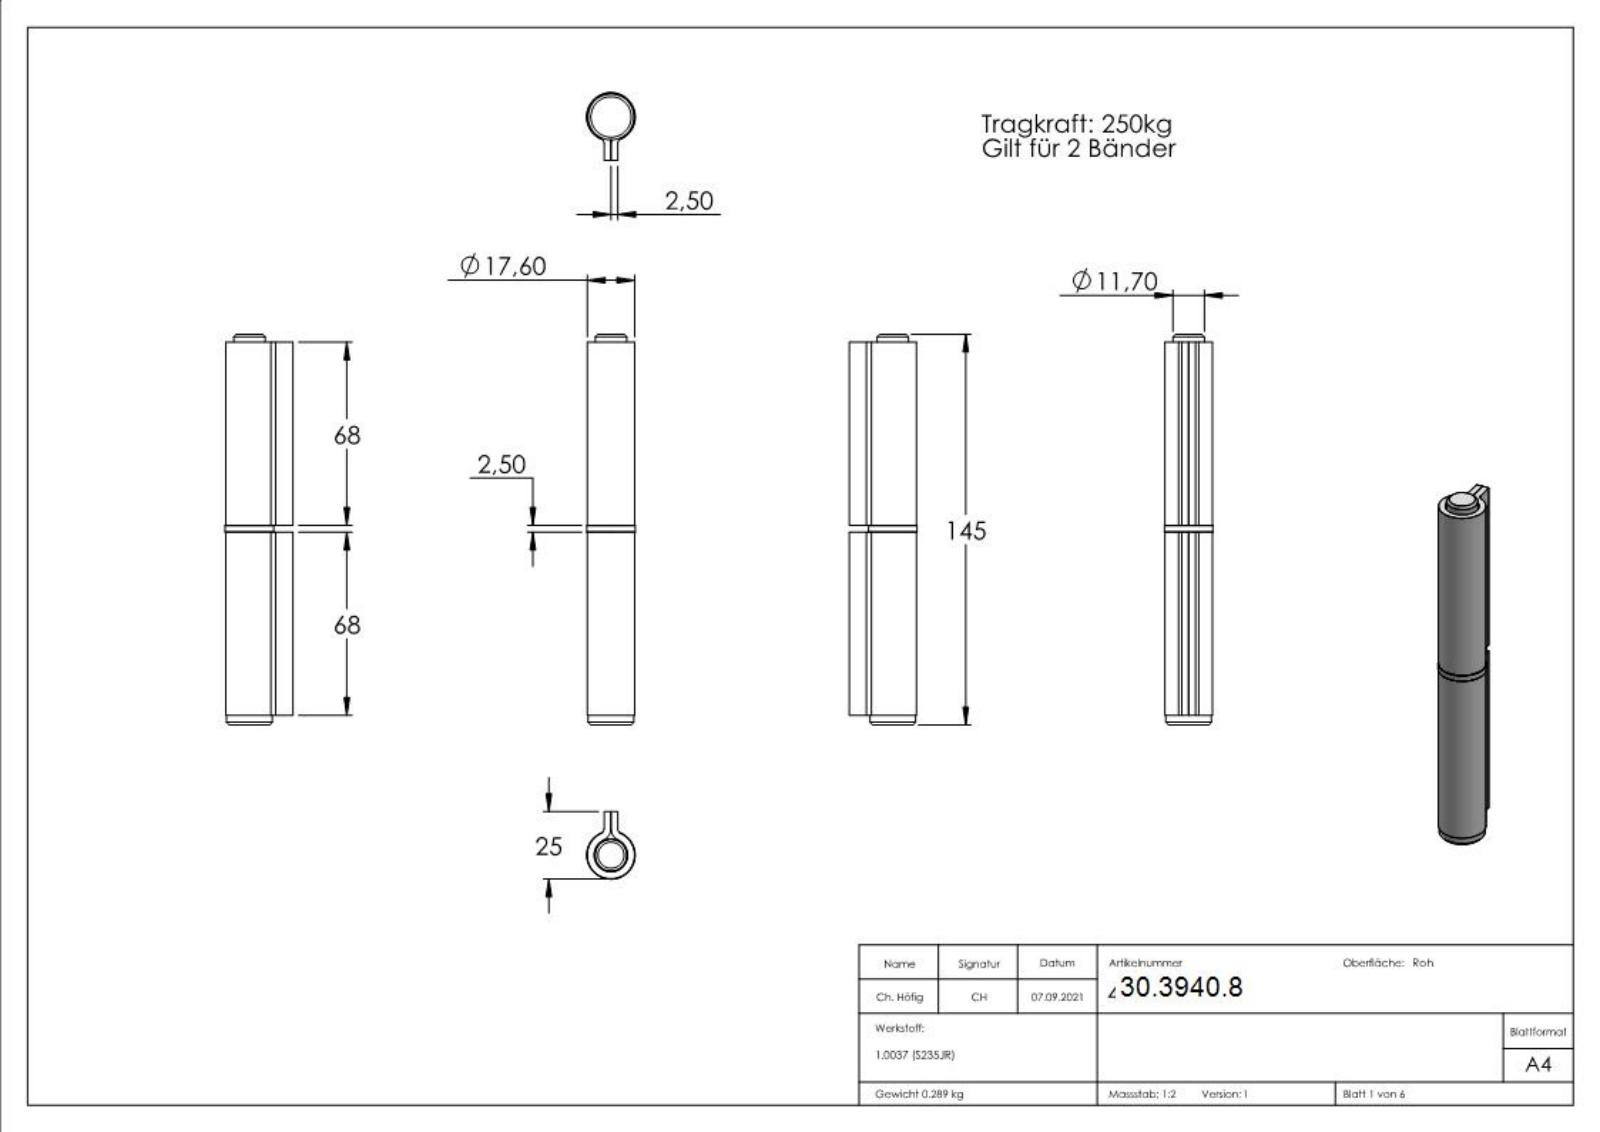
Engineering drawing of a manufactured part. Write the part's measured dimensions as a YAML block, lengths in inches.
part_name: "405-xx Teil1_405-14 Teil1; 405-14; 405-xx Teil1; 405-xx Teil3_405-14 Teil3 (+5 more)"
step_written_by: "SolidWorks 2018 (CONFIG_CONTROL_DESIGN)"
units: inches
bodies: {solids: 4, faces: 310, planar: 161, cylindrical: 38, other: 111}
overall_size: [5.709, 0.992, 0.709]
volume: 2.263
surface_area: 37.52
round_holes:
  - {diameter: 0.472, count: 1}
  - {diameter: 0.496, count: 1}
round_bosses_or_shafts:
  - {diameter: 0.709, count: 1}
  - {diameter: 0.693, count: 1}
  - {diameter: 0.669, count: 1}
  - {diameter: 0.461, count: 1}
partial_cylinders:
  - {radius: 0.079, count: 2}
  - {radius: 0.177, count: 2}
  - {radius: 0.252, count: 1}
face_to_face_distances: [0.098, 0.102, 0.201, 2.776, 2.677, 0.138, 2.815, 2.913, 5.591, 5.453]
